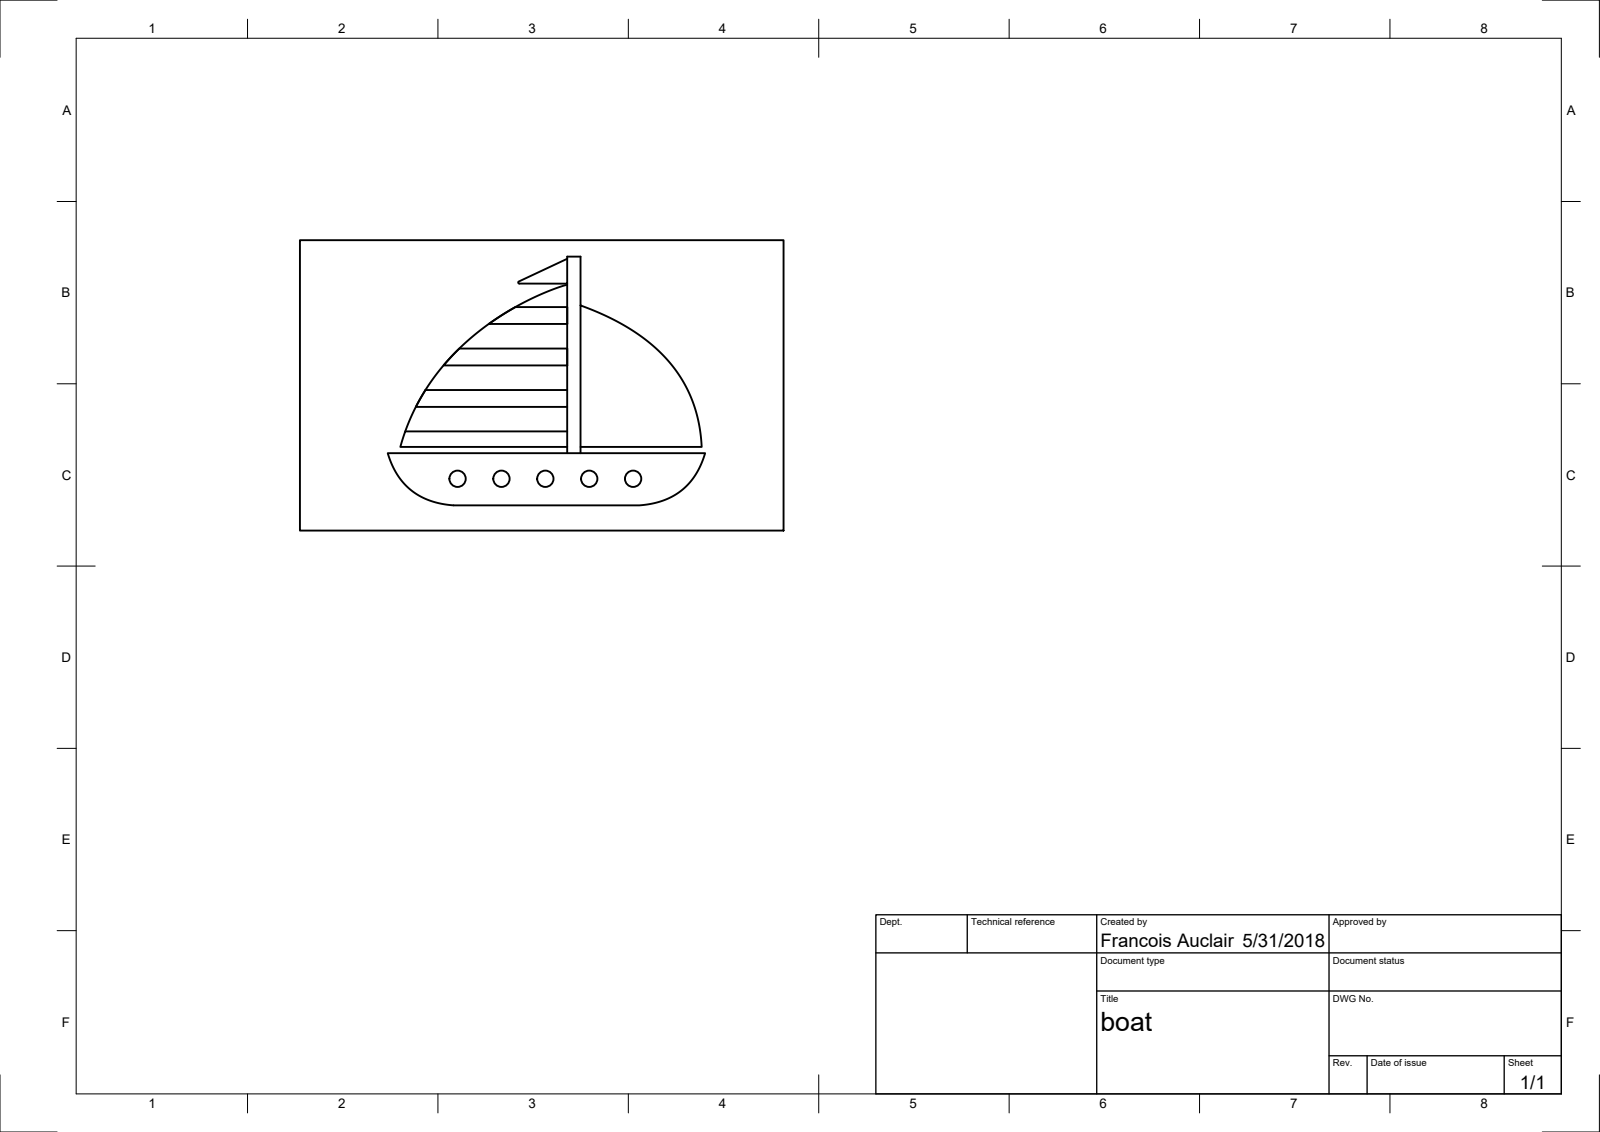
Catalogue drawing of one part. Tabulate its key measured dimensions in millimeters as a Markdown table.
| quantity | value |
| --- | --- |
| part name | WILDCARD FORM |
| STEP written by | SolidWorks 2024 (CONFIG_CONTROL_DESIGN) |
| units | millimeters |
| bodies | 1 solid, 16 faces (2 planar, 7 cylindrical, 7 other) |
| overall size | 255.37 × 165.77 × 93.7 |
| volume | 2 009 000 mm³ |
| surface area | 97 498 mm² |
| partial cylindrical surfaces (radius × count) | 3.7 × 2, 72.7 × 1, 329.66 × 1, 556.3 × 1 |
| main face-to-face distances | 93.7 |
